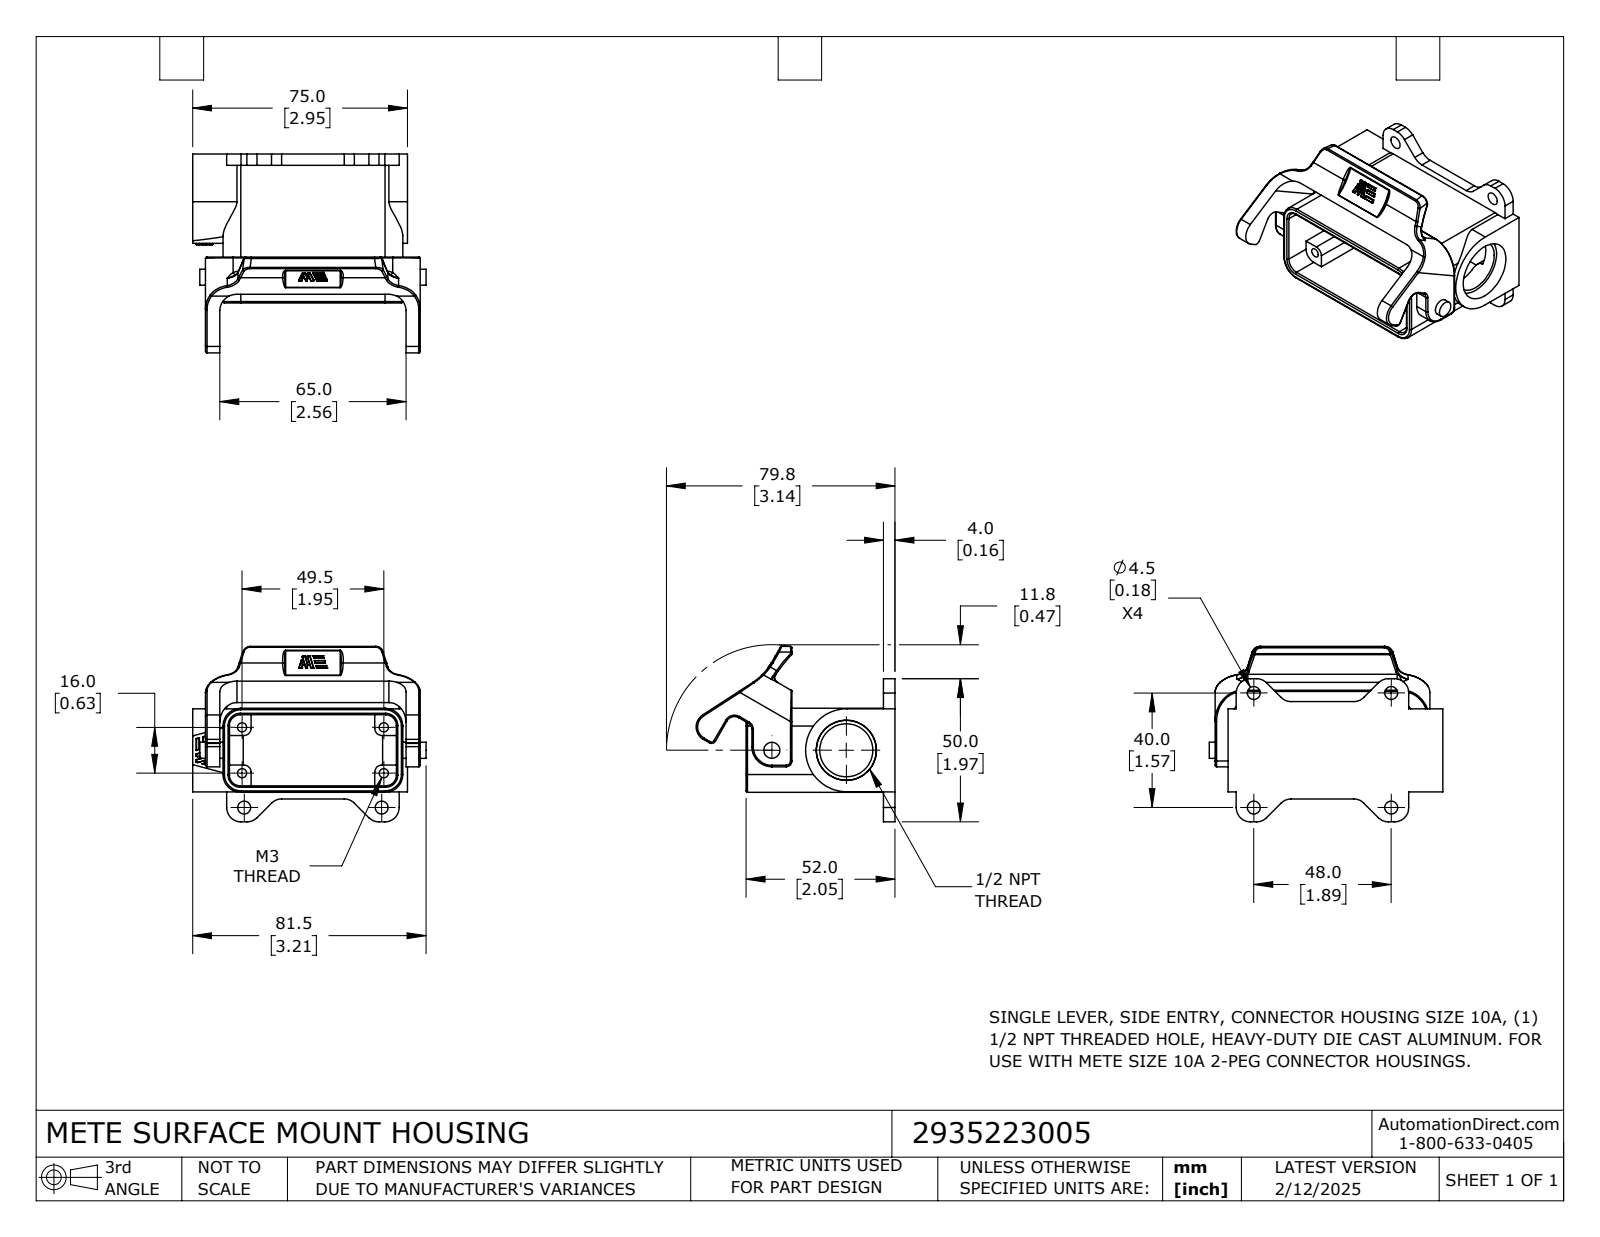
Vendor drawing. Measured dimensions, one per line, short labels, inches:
name: 2935223005
written by: SolidWorks 2024 (CONFIG_CONTROL_DESIGN)
unit: in
bodies: 1 solid, 392 faces (153 planar, 169 cylindrical, 70 other)
size: 3.209 × 2.734 × 2.411
volume: 3.114 in³; area: 48.17 in²
holes: 4× ⌀0.126, 4× ⌀0.177, 1× ⌀0.729
bosses: 1× ⌀0.22
rounds: 30× R0.02, 25× R0.004, 15× R0.197, 7× R0.098, 4× R0.148, 4× R0.244, 2× R0.039, 2× R0.079
face distances: 0.089, 1.065, 1.154, 0.976, 0.157, 2.953, 0.177, 0.197, 0.429, 2.756
hole spacings: 0.473, 1.103, 1.977, 2.213, 0.63, 1.575, 1.89, 1.949
